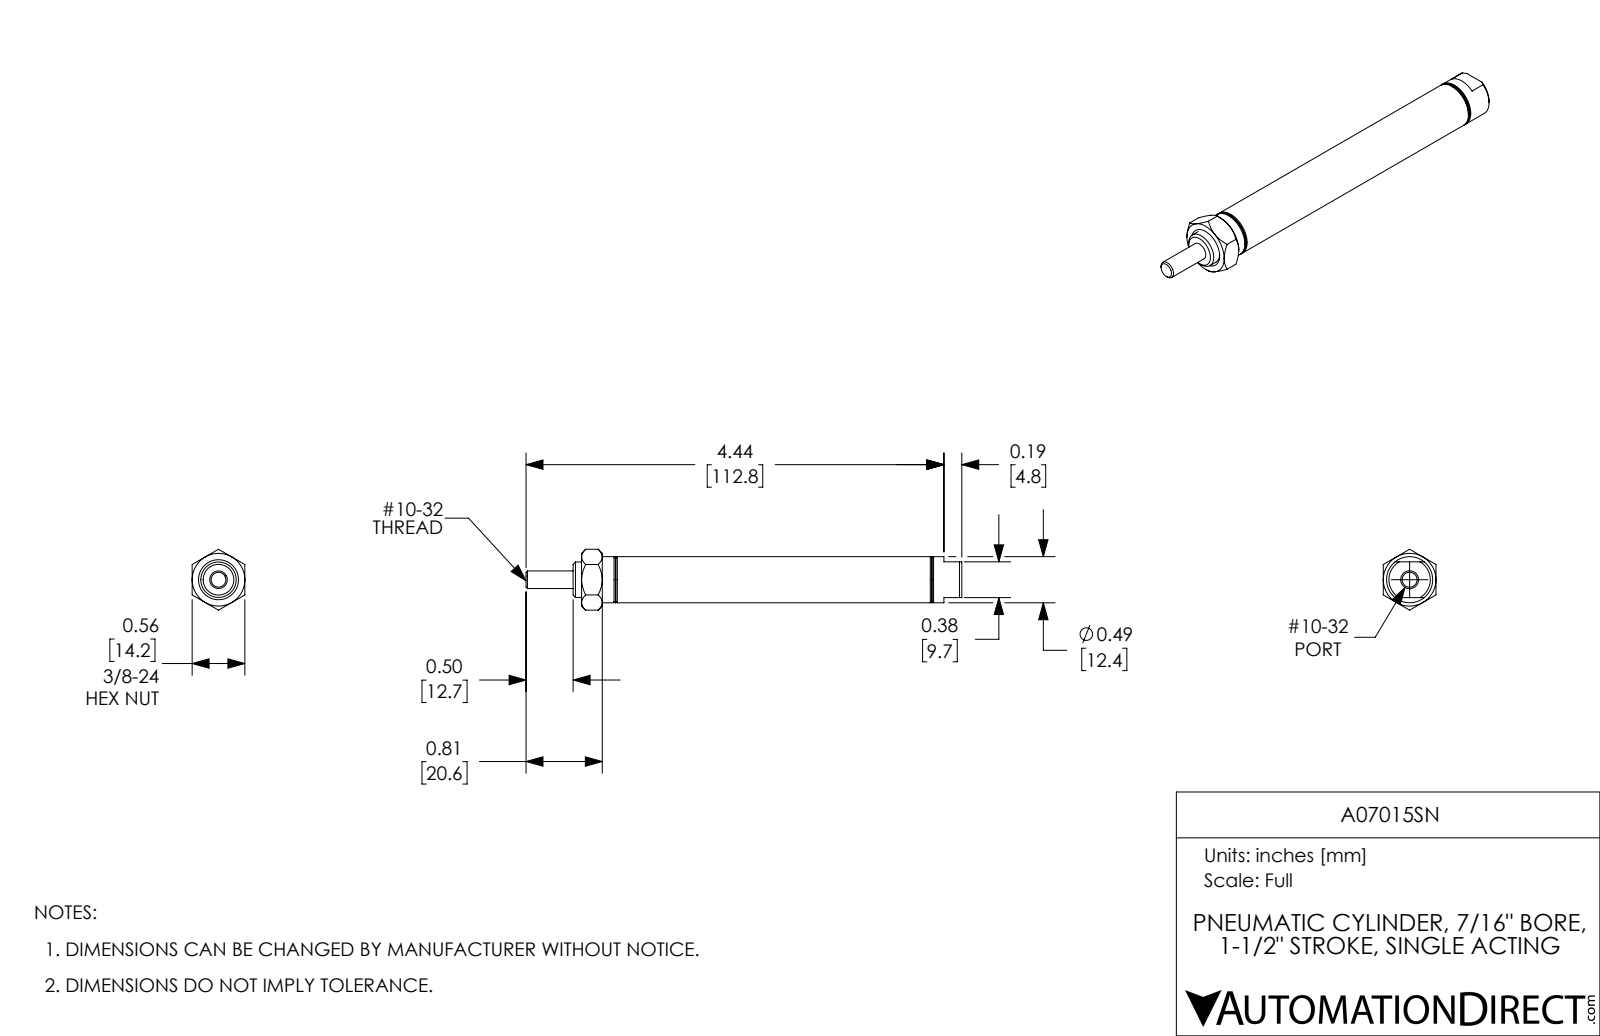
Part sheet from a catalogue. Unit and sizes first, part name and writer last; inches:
Units: inches
Overall size (bounding box): 4.63 × 0.647 × 0.56
Round holes (diameter × count): ⌀0.159 ×1, ⌀0.187 ×1, ⌀0.19 ×1, ⌀0.375 ×1, ⌀0.437 ×1
Round bosses / shafts (diameter × count): ⌀0.49 ×1, ⌀0.376 ×1
Main face-to-face distances: 0.56, 2.91, 0.5, 2.41, 2, 1.5, 0.91, 0.91, 1.41, 2.91
Volume: 0.598 in³ · Surface area: 14.54 in²
Bodies: 3 solids, 84 faces (25 planar, 26 cylindrical, 33 other)
Part name (STEP PRODUCT): A07015SN; A07015SN_Mounting Nut_D-801; A07015SN-MainBody; A07015SN-Rod
STEP written by: SolidWorks 2017 (AUTOMOTIVE_DESIGN)
